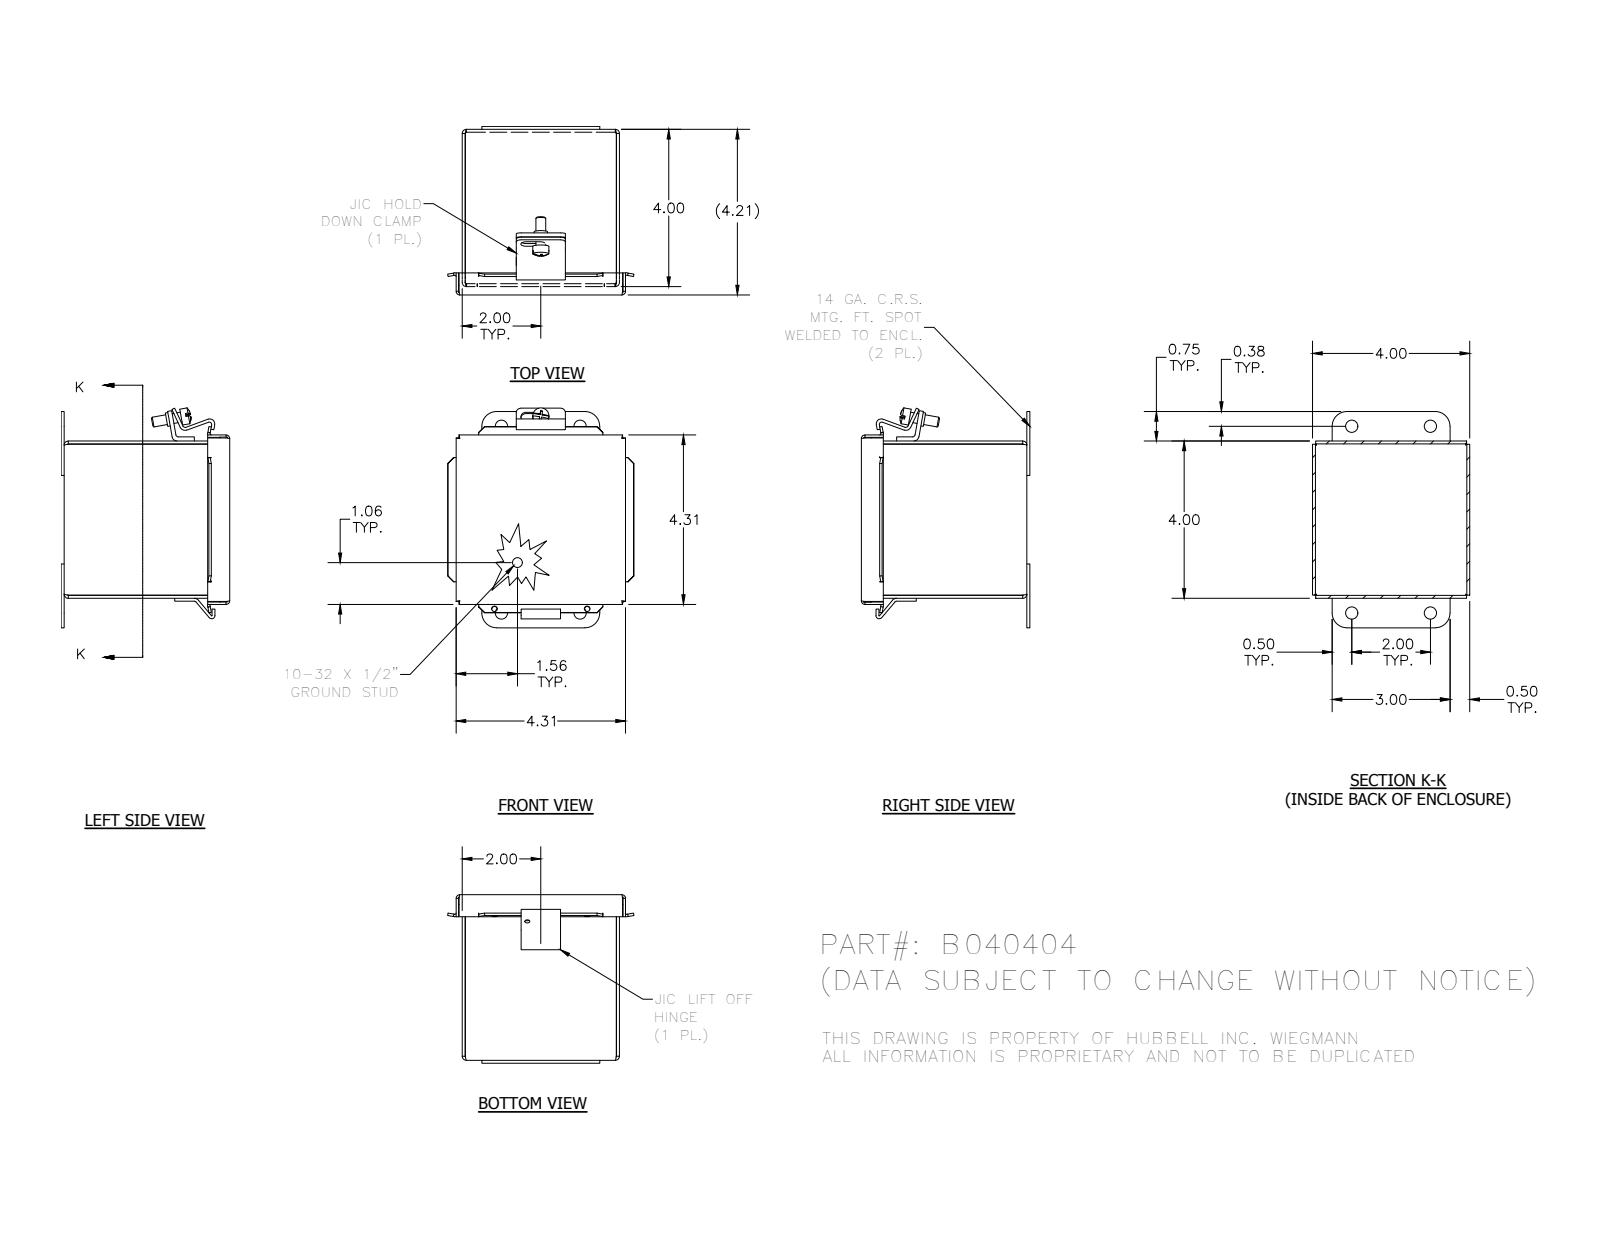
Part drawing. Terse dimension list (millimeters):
name: B040404; 3481; C1001; H4050550 (+6 more)
written by: Autodesk Inventor 2012 (AUTOMOTIVE_DESIGN)
unit: mm
bodies: 11 solids, 310 faces (215 planar, 65 cylindrical, 30 other)
size: 142.1 × 120.4 × 108.9
volume: 172 200 mm³; area: 179 500 mm²
holes: 4× ⌀7.9, 2× ⌀3.6, 1× ⌀3.2, 1× ⌀5
bosses: 2× ⌀6.4, 1× ⌀10.4, 1× ⌀8.7, 1× ⌀4.8
rounds: 16× R0.8, 8× R2.4, 8× R2.7, 4× R3.2, 4× R9.5, 3× R1.6, 3× R3.2, 2× R3.4
face distances: 1.9, 99.7, 101.6, 97.8, 105.4, 107, 1.6, 103.5, 105.1, 1.9
hole spacings: 50.8, 120.7, 128.8, 130.9, 59.9
